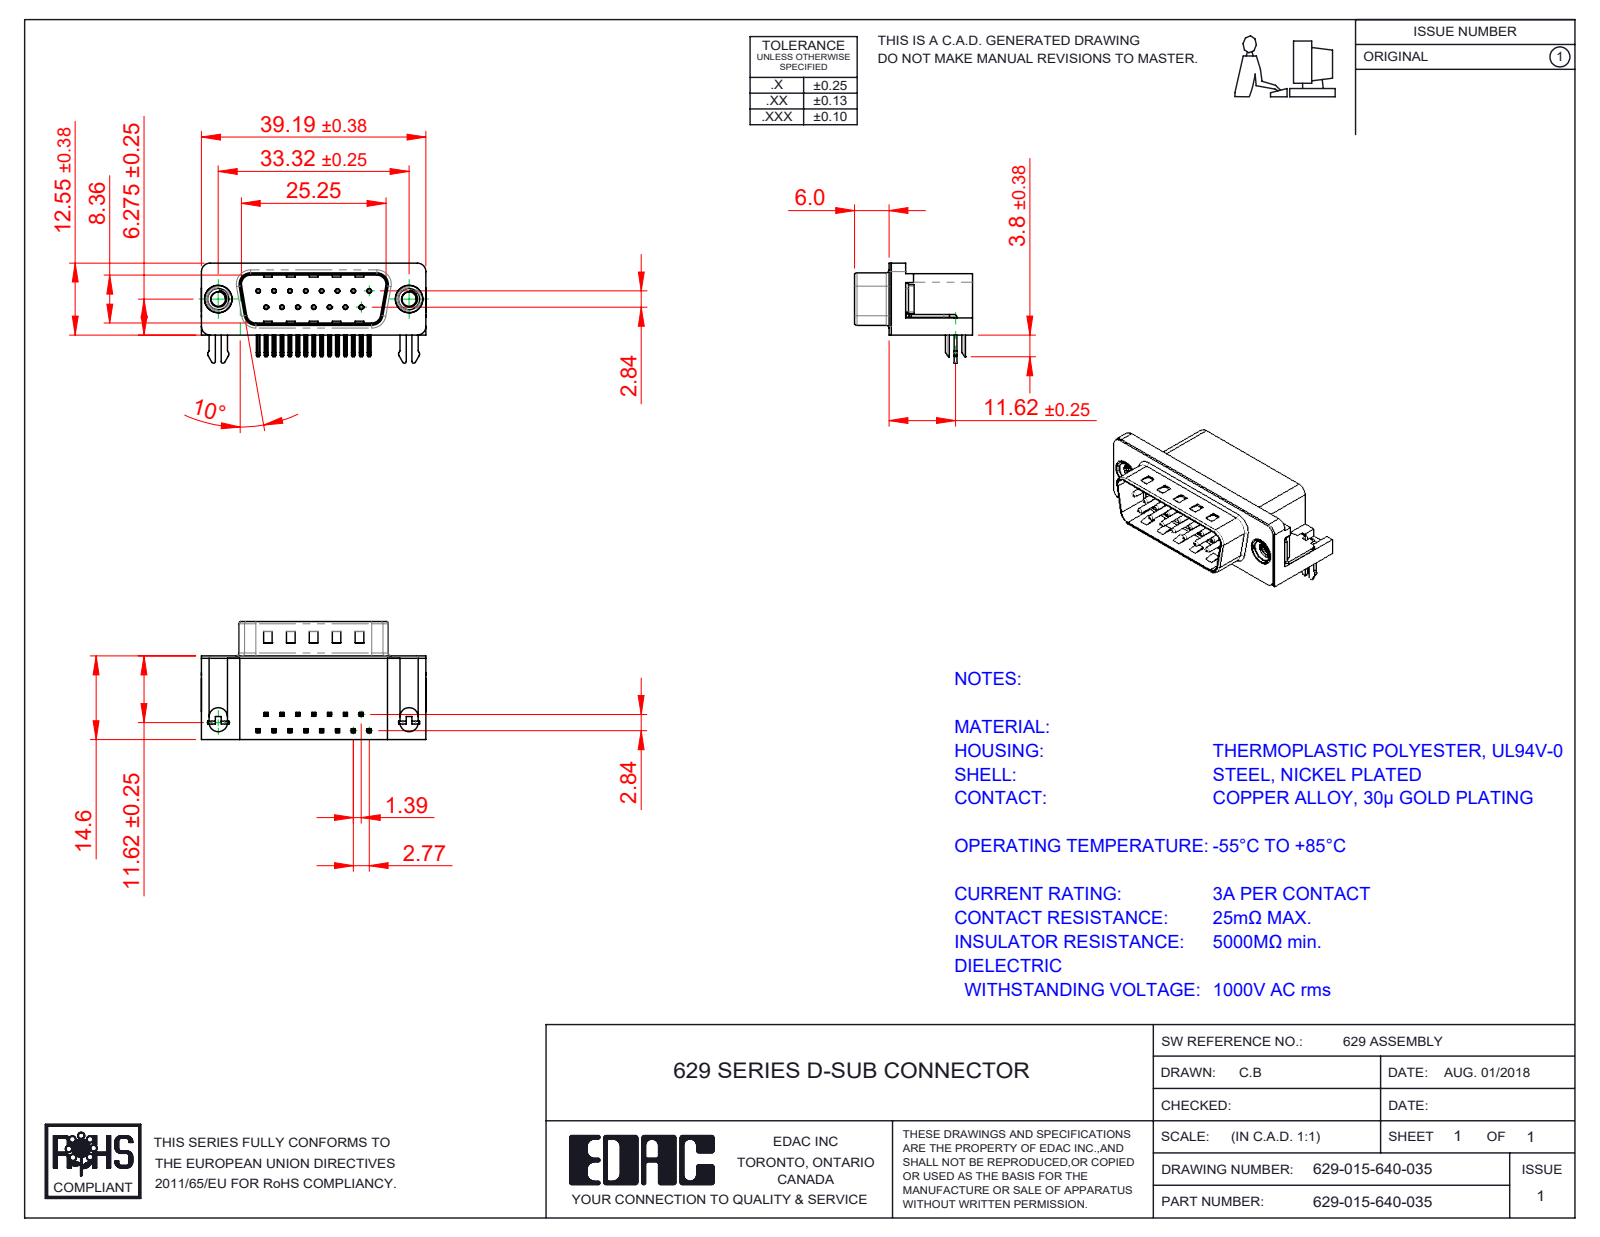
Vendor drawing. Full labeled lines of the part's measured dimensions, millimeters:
Part name (STEP PRODUCT): 629-015-640-035; 629 2 Prong Board Lock; 629 M3 Threaded Rivet; 629 Contact Bottom (+3 more)
STEP written by: SolidWorks 2020 (CONFIG_CONTROL_DESIGN)
Units: millimetres
Bodies: 21 solids, 1515 faces (923 planar, 457 cylindrical, 135 other)
Overall size (bounding box): 39.22 × 20.6 × 17.48
Volume: 5 075 mm³ · Surface area: 6 082 mm²
Round holes (diameter × count): ⌀0.35 ×15, ⌀0.8 ×15, ⌀2.5 ×2, ⌀4 ×2, ⌀4.8 ×2, ⌀5 ×2
Round bosses / shafts (diameter × count): ⌀0.75 ×15, ⌀4.9 ×2, ⌀4.75 ×2, ⌀3.9 ×2
Partial cylindrical surfaces — rounded edges, fillets, slot ends (radius × count): R0.25 ×68, R0.12 ×30, R1 ×16, R0.5 ×14, R1.6 ×8, R1.5 ×6, R0.32 ×4, R0.9 ×4
Main face-to-face distances: 0.4, 14.2, 10.35, 2.1, 14.6, 10.46, 1.7, 10.86, 8.76, 0.5
Hole centre spacings: 3.16, 2.77, 5.54, 8.31, 11.08, 5.03, 5.04, 7.48
